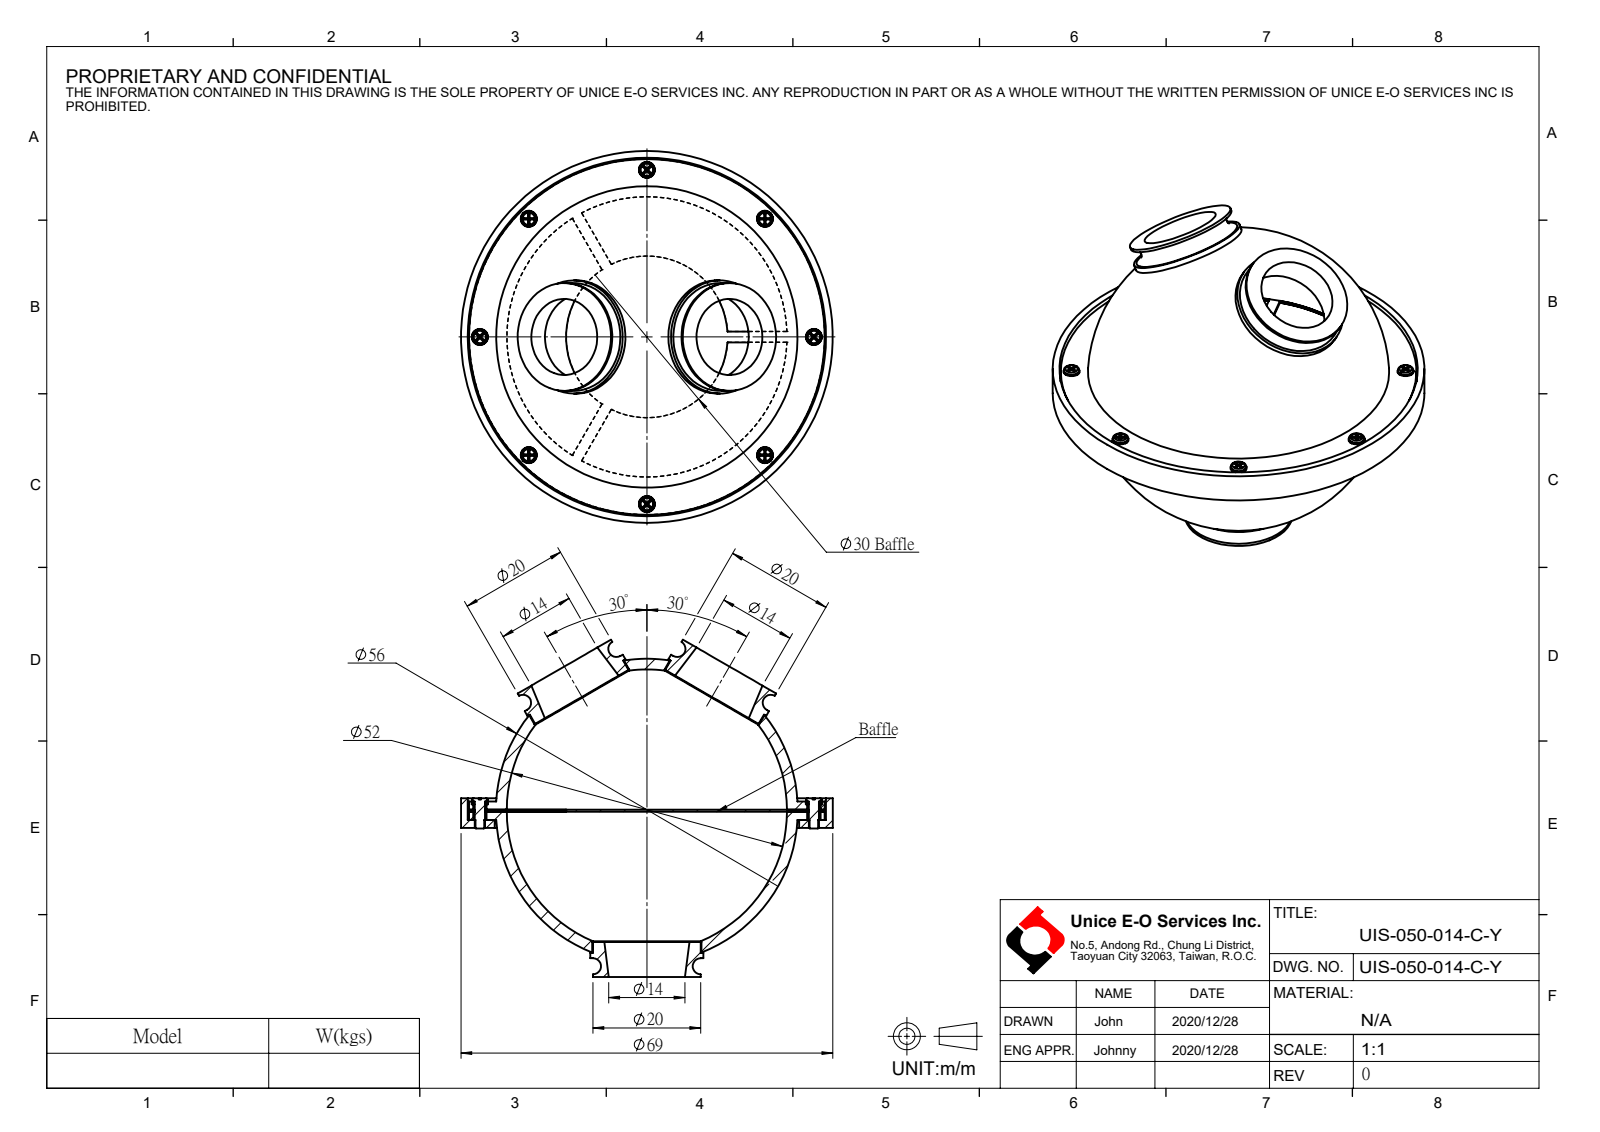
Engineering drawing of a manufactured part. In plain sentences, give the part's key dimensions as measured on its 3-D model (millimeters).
The part is named "UIS-050-014-N-Y". Its 3-D file was written by "SolidWorks 2020 (CONFIG_CONTROL_DESIGN)". It is 0 solids with 217 faces: 76 planar, 67 cylindrical and 74 other. Overall it measures 69 by 69 by 62.6 millimeters. Round holes: 8 of diameter 3, 4 of diameter 2.5, 1 of diameter 52, 1 of diameter 56.5, 1 of diameter 66.5. Round bosses or shafts: 8 of diameter 1.9, 3 of diameter 21, 3 of diameter 20, 2 of diameter 20.3, 1 of diameter 69, 1 of diameter 66. The main face-to-face distances are 1.5, 3.4, 1.9, 0.4, 3, 4.9, 5.5, 4, 2.5, 2.1. The hole center spacings are 23.73, 31, 43.84, 57.28, 62.
